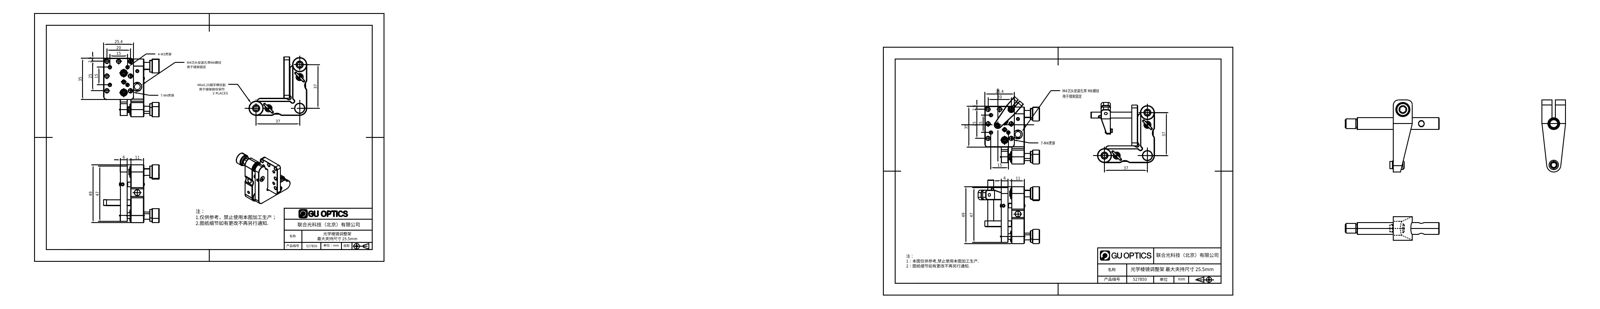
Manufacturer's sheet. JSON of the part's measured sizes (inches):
{"part_name": "527850", "step_written_by": "SolidWorks 2020 (CONFIG_CONTROL_DESIGN)", "units": "inches", "bodies": {"solids": 0, "faces": 379, "planar": 166, "cylindrical": 89, "other": 124}, "overall_size": [2.271, 2.146, 1.858], "round_holes": [[0.374, 3], [0.472, 2], [0.091, 1]], "round_bosses_or_shafts": [[0.098, 8], [0.236, 7], [0.13, 7], [0.118, 6], [0.339, 3], [0.197, 3], [0.157, 3], [0.295, 2]], "partial_cylinders_radius": [[0.079, 11], [0.197, 5], [0.031, 4], [0.098, 4], [0.118, 3], [0.031, 2], [0.059, 1], [0.063, 1]], "face_to_face_distances": [0.433, 0.551, 0.787, 0.236, 0.197, 0.354, 0.118, 0.472, 0.098, 0.571], "hole_center_spacings": [1.457, 2.06]}
